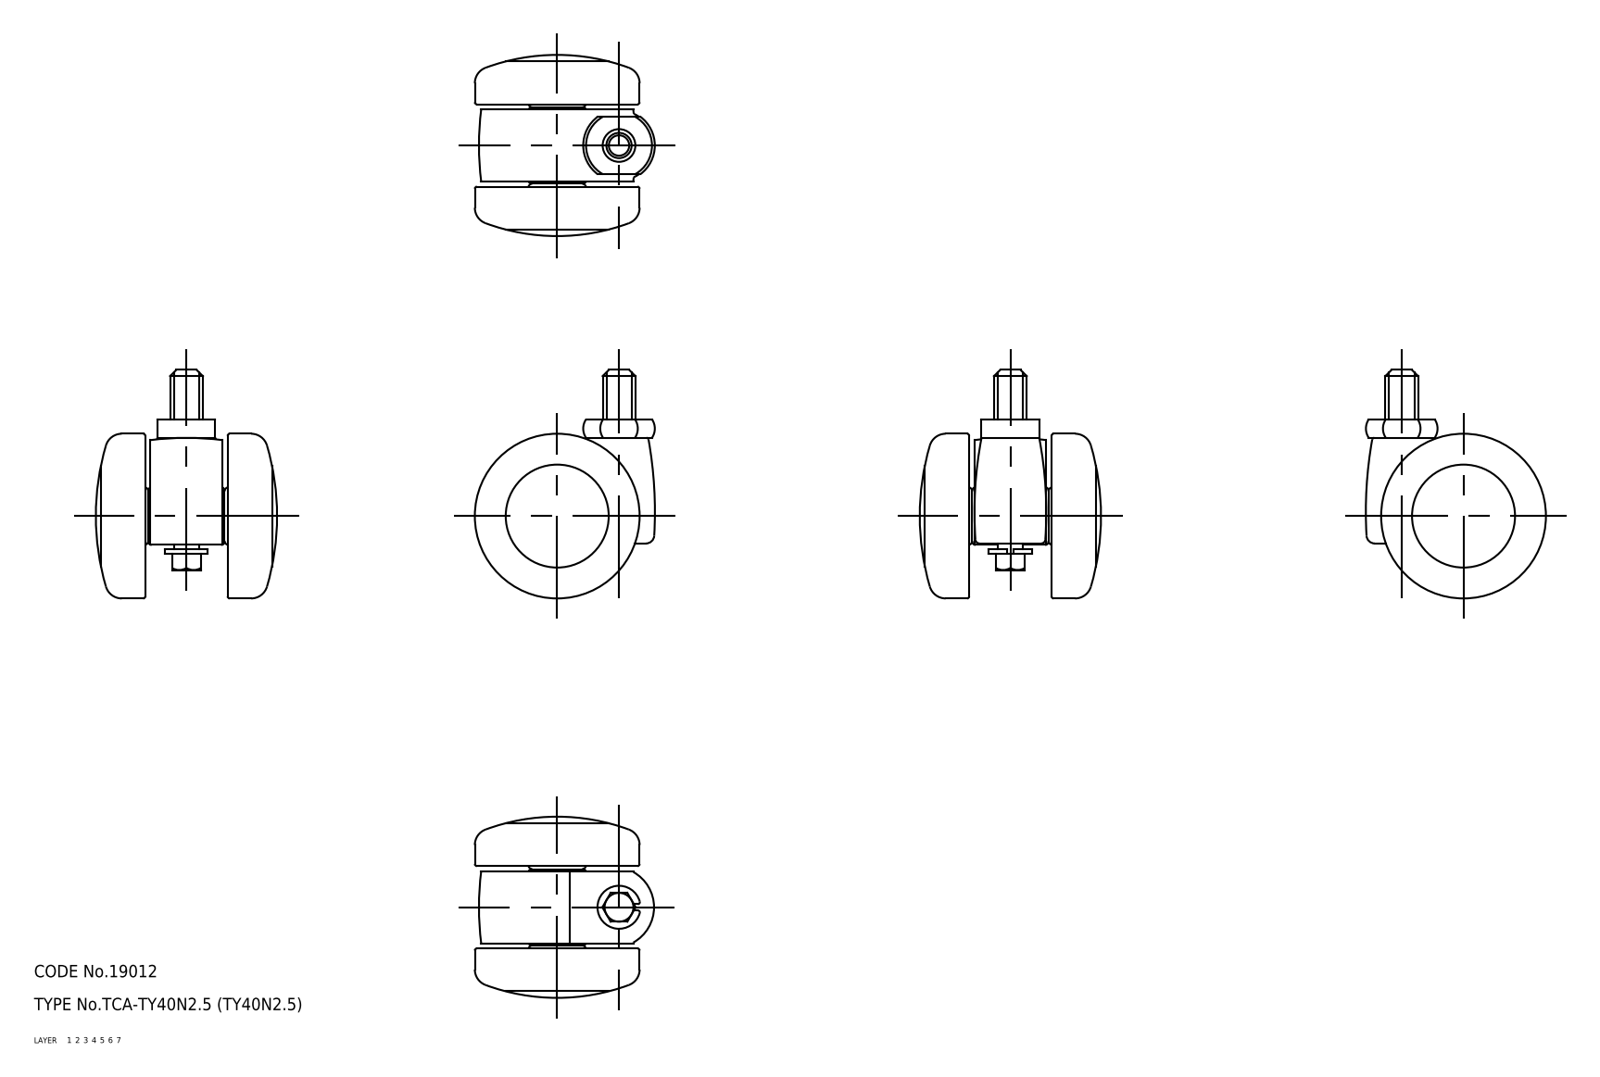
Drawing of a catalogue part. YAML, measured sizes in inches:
part_name: "wheel; main shaft; TY40N2_5_10293_36"
step_written_by: "CADfix (AUTOMOTIVE_DESIGN)"
units: inches
bodies: {solids: 4, faces: 117, planar: 0, cylindrical: 0, other: 117}
overall_size: [2.185, 1.732, 1.721]
volume: 2.351
surface_area: 26.96
